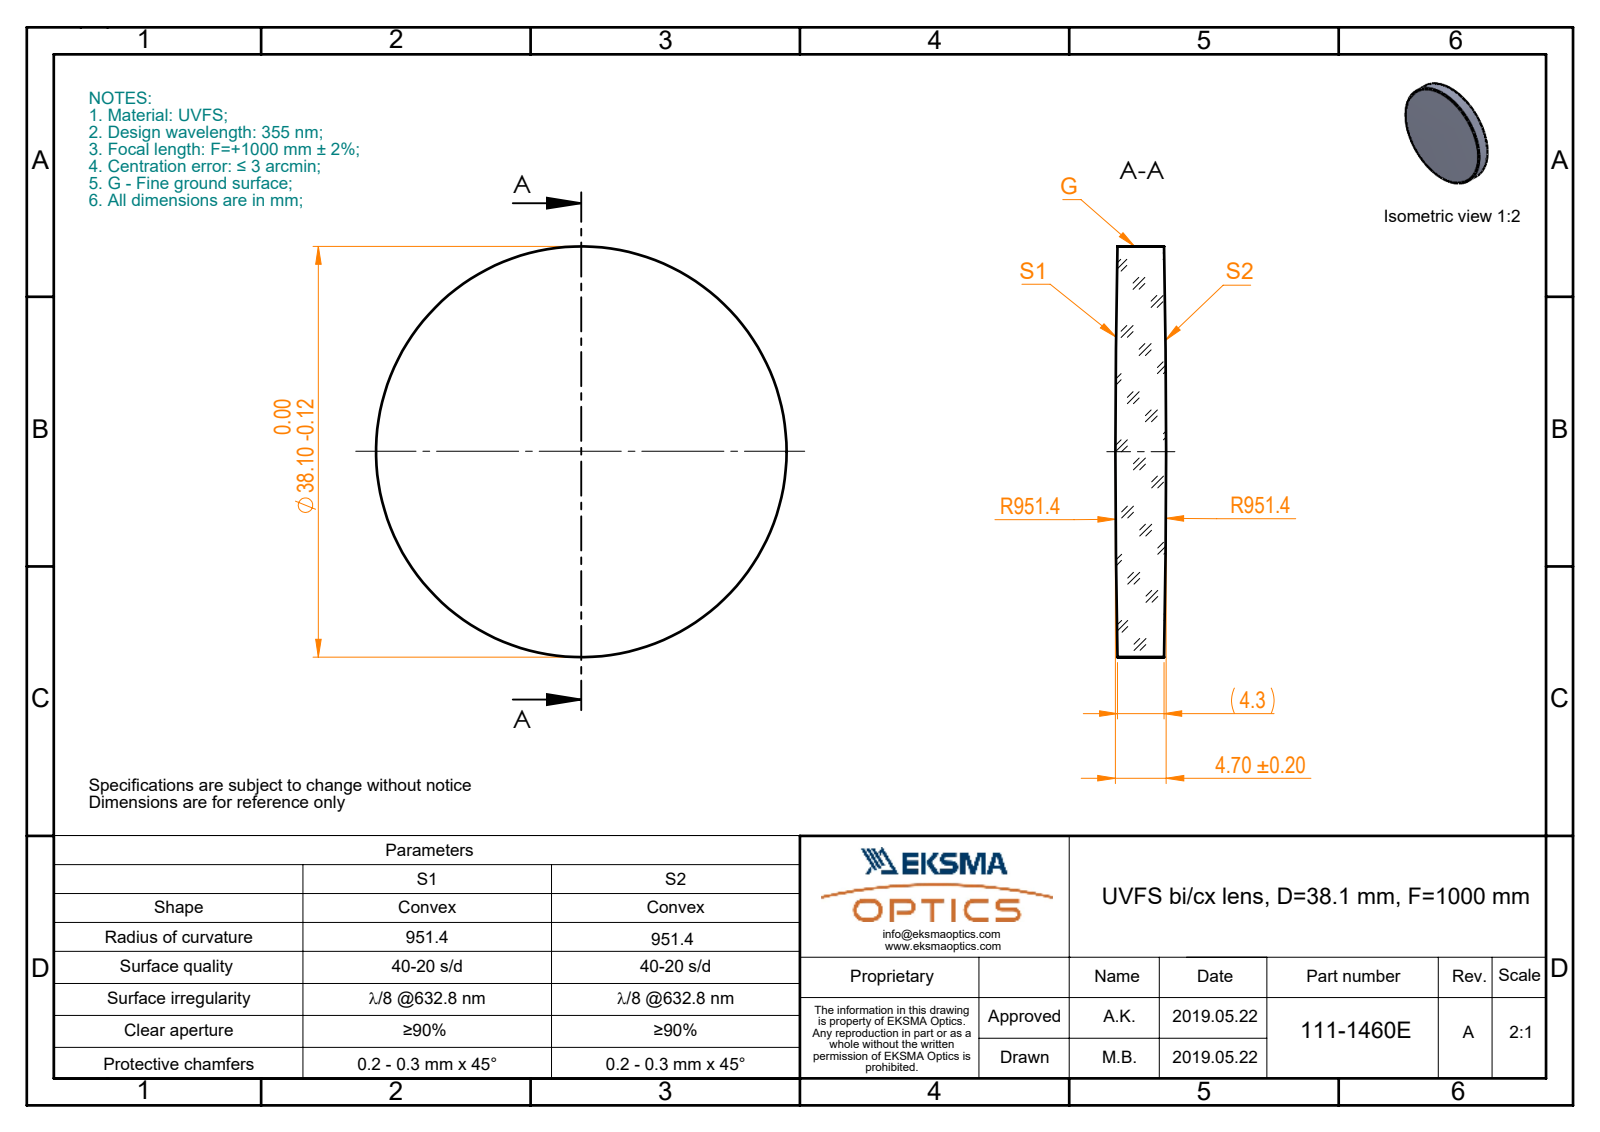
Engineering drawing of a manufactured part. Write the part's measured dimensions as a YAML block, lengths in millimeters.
part_name: "111-1460E UVFS bi-cx 38.1 F1000"
step_written_by: "SolidWorks 2017 (CONFIG_CONTROL_DESIGN)"
units: millimeters
bodies: {solids: 1, faces: 6, planar: 0, cylindrical: 2, other: 4}
overall_size: [38.1, 38.1, 4.7]
volume: 5141
surface_area: 2797
round_bosses_or_shafts:
  - {diameter: 38.1, count: 1}
